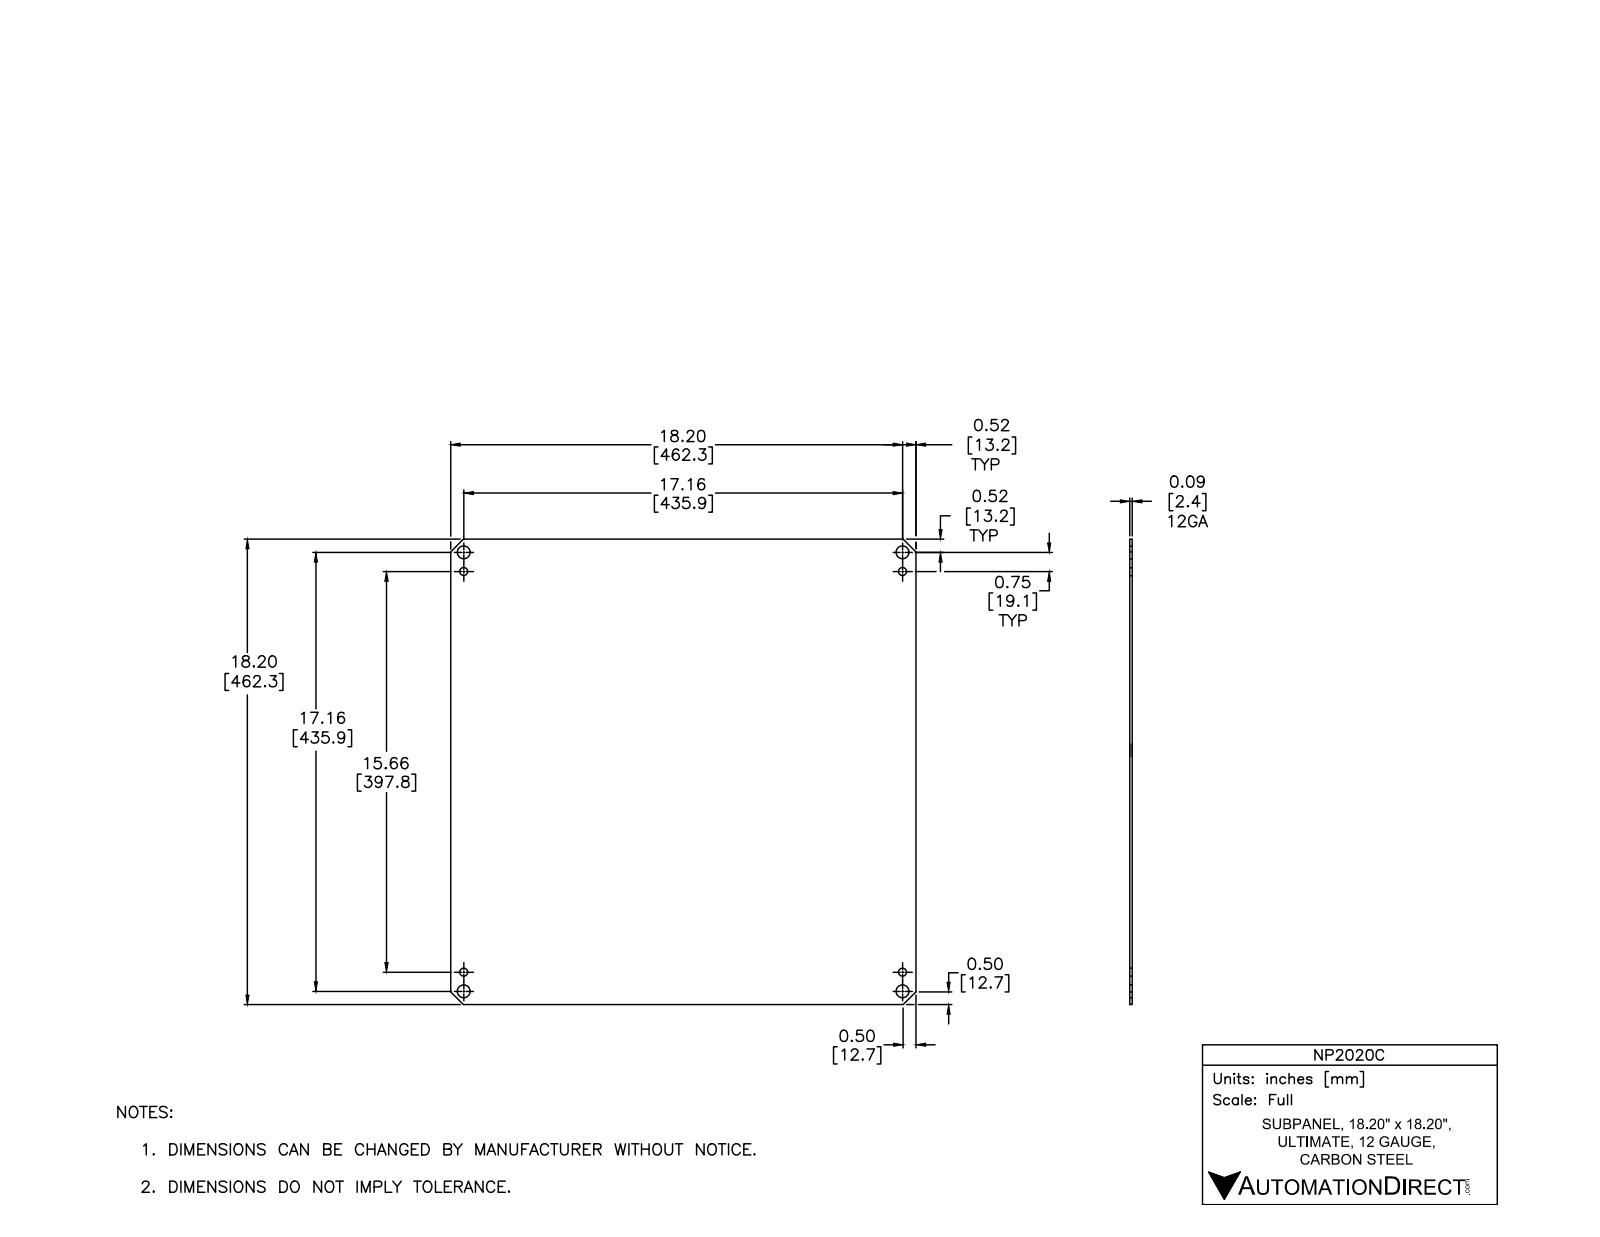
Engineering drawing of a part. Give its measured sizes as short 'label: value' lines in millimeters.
name: NP2020C
written by: Autodesk Inventor 2012 (AUTOMOTIVE_DESIGN)
unit: mm
bodies: 1 solid, 18 faces (10 planar, 8 cylindrical, 0 other)
size: 462.3 × 462.3 × 2.4
volume: 506 400 mm³; area: 430 300 mm²
holes: 4× ⌀8, 4× ⌀12.7
face distances: 2.4, 462.3, 635.7, 635.7
hole spacings: 435.9, 19.1, 416.8, 436.3, 603.1, 397.8, 590.1, 616.4
